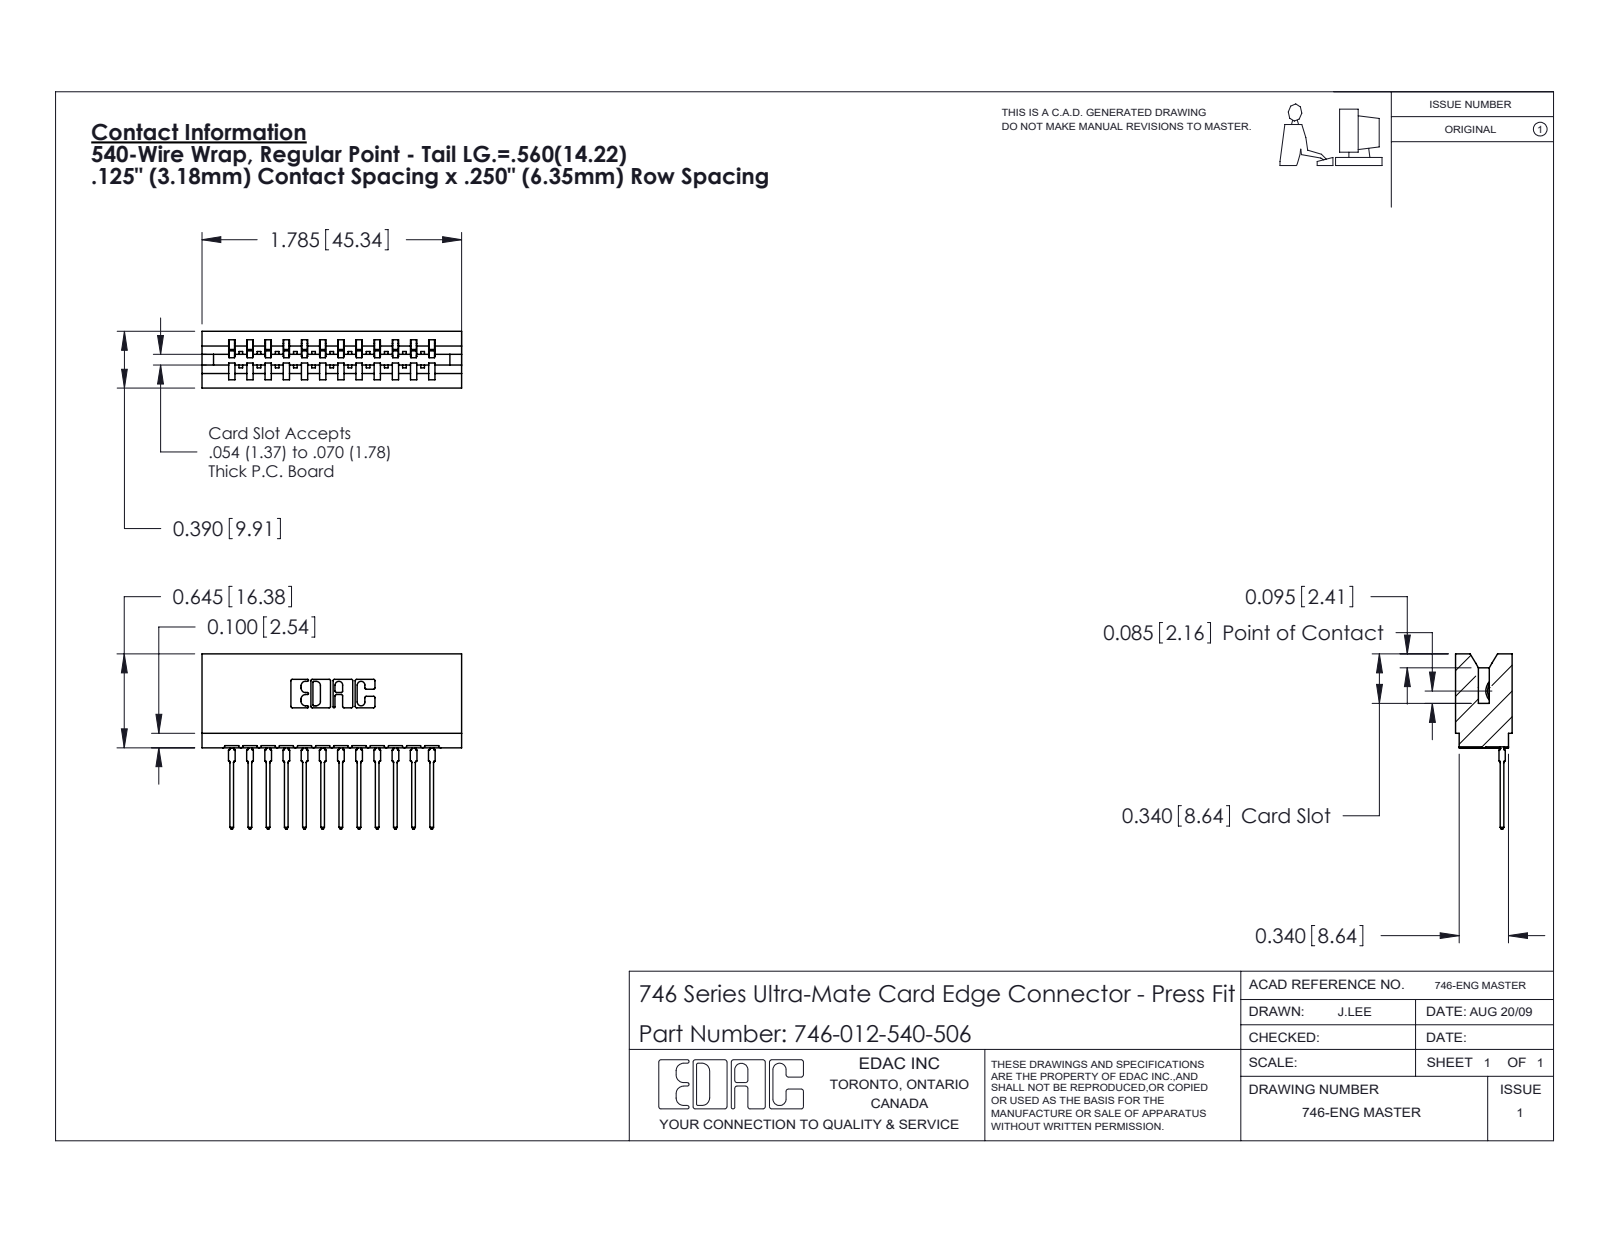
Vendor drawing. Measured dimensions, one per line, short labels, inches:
name: 746-012-540-506; 746-292-001_540; 746 Part_.340 Slot Depth - 06
written by: SolidWorks 2020 (CONFIG_CONTROL_DESIGN)
unit: in
bodies: 13 solids, 1394 faces (812 planar, 270 cylindrical, 312 other)
size: 1.785 × 1.204 × 0.39
volume: 0.322 in³; area: 10.57 in²
rounds: 24× R0.021, 22× R0.01, 13× R0.015, 6× R0.007, 6× R0.031, 4× R0.005, 4× R0.011, 3× R0.026
face distances: 0.25, 0.5, 0.057, 0.333, 0.125, 0.39, 0.042, 0.125, 0.292, 0.542
